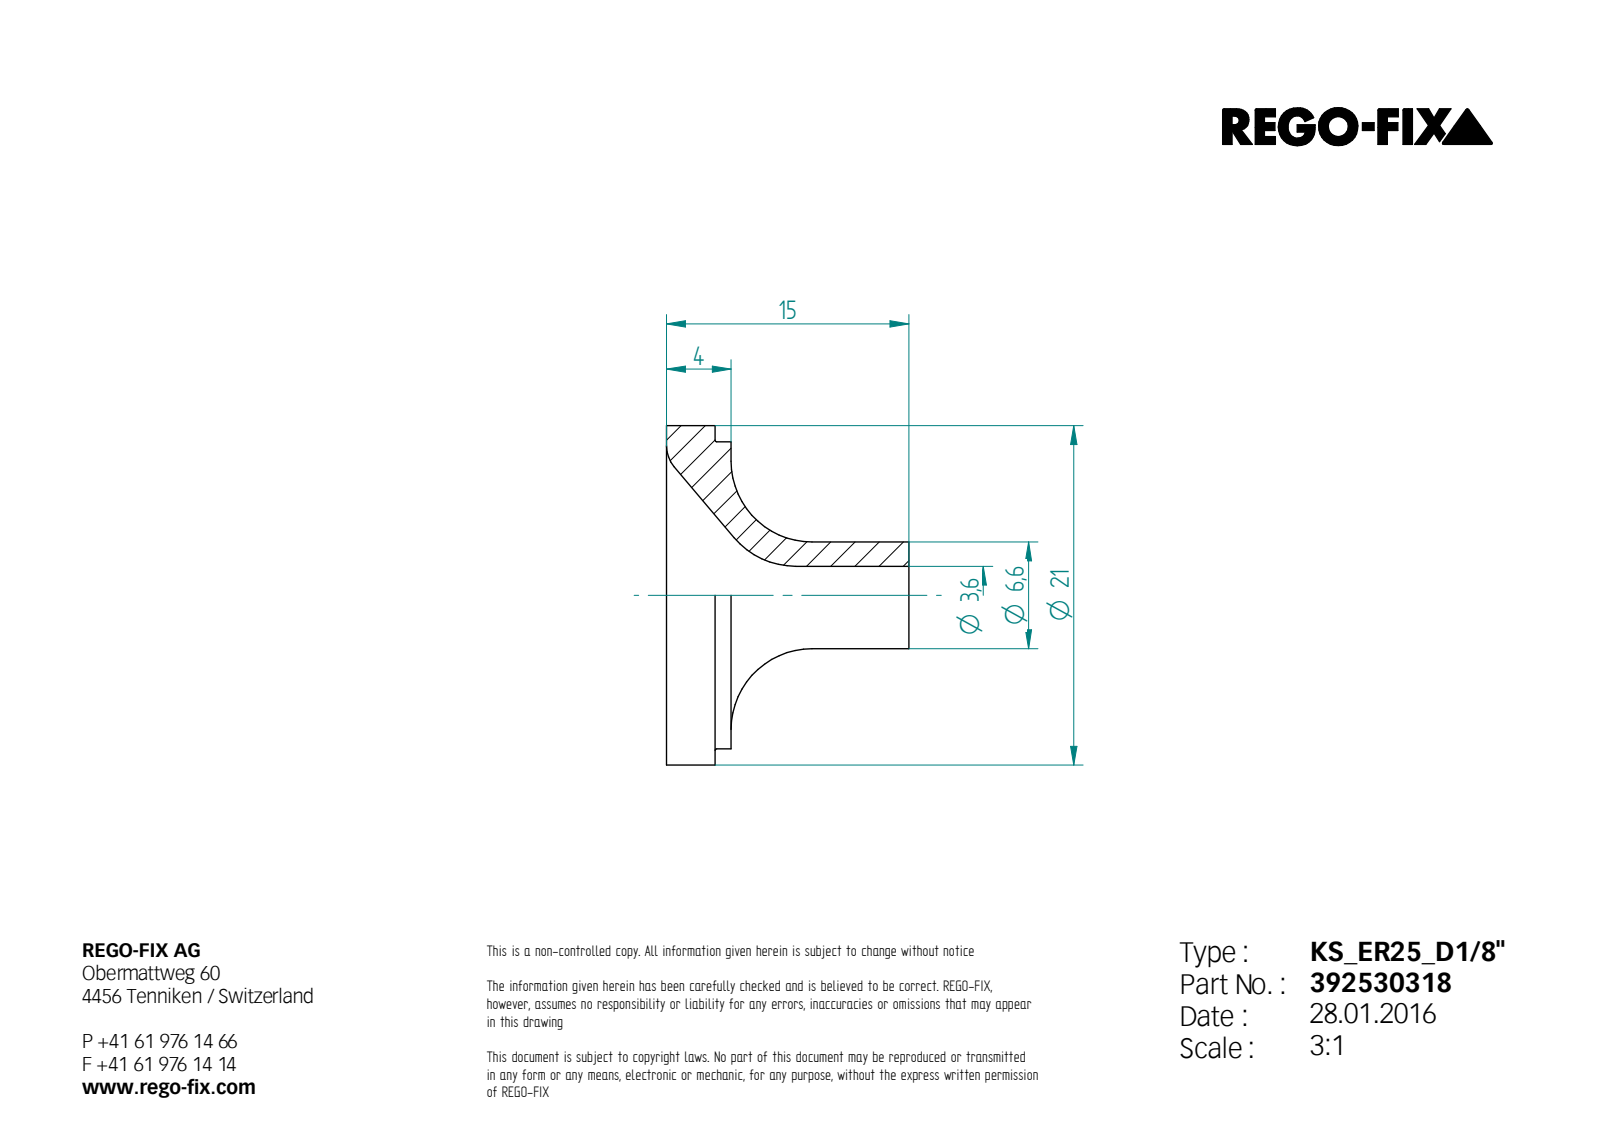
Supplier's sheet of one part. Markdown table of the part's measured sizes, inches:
| quantity | value |
| --- | --- |
| STEP written by | Unknown (AUTOMOTIVE_DESIGN) |
| units | inches |
| bodies | 1 solid, 13 faces (4 planar, 4 cylindrical, 5 other) |
| overall size | 0.827 × 0.827 × 0.591 |
| volume | 0.073 in³ |
| surface area | 2.003 in² |
| round holes (diameter × count) | 0.142 × 1 |
| round bosses / shafts (diameter × count) | 0.827 × 1, 0.748 × 1, 0.26 × 1 |
| main face-to-face distances | 0.157, 0.118, 0.039, 0.591, 0.472, 0.433 |
